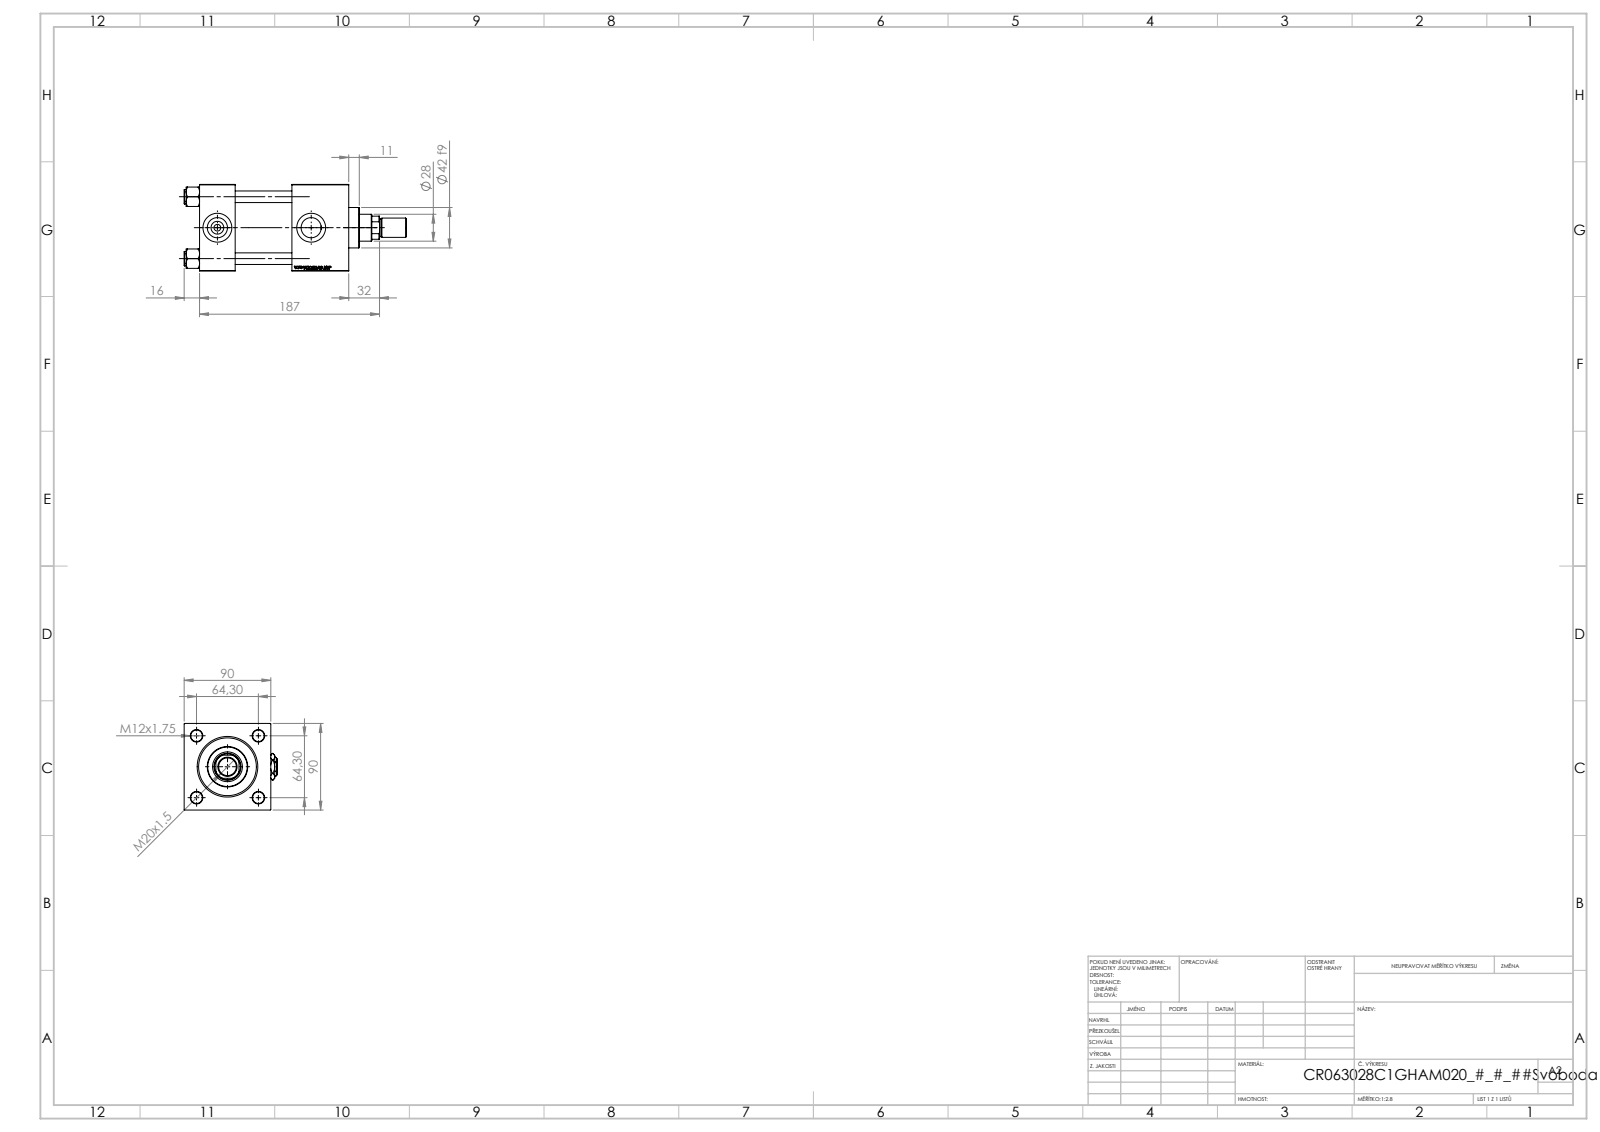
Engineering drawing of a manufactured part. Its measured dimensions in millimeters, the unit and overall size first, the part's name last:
Units: millimetres
Overall size (bounding box): 231 × 97 × 90
Round holes (diameter × count): ⌀12 ×4, ⌀7 ×2, ⌀20.96 ×2, ⌀30 ×2, ⌀18.5 ×1, ⌀28 ×1, ⌀31 ×1, ⌀50 ×1, ⌀60 ×1, ⌀63 ×1
Round bosses / shafts (diameter × count): ⌀15 ×4, ⌀69 ×1, ⌀42 ×1, ⌀20 ×1, ⌀18 ×1
Partial cylindrical surfaces — rounded edges, fillets, slot ends (radius × count): R13.5 ×1
Main face-to-face distances: 90, 59, 37, 118, 155, 96, 126.3, 89.3, 30.3, 28.7
Hole centre spacings: 45.47, 64.3, 90.93, 97.5
Volume: 951 109 mm³ · Surface area: 183 686 mm²
Bodies: 13 solids, 1210 faces (554 planar, 94 cylindrical, 562 other)
Part name (STEP PRODUCT): V215CR_VCP_C; NUT_M5_C; V215CR_C_Body; ROD_END_AH (+3 more)
STEP written by: SolidWorks 2019 (CONFIG_CONTROL_DESIGN)
